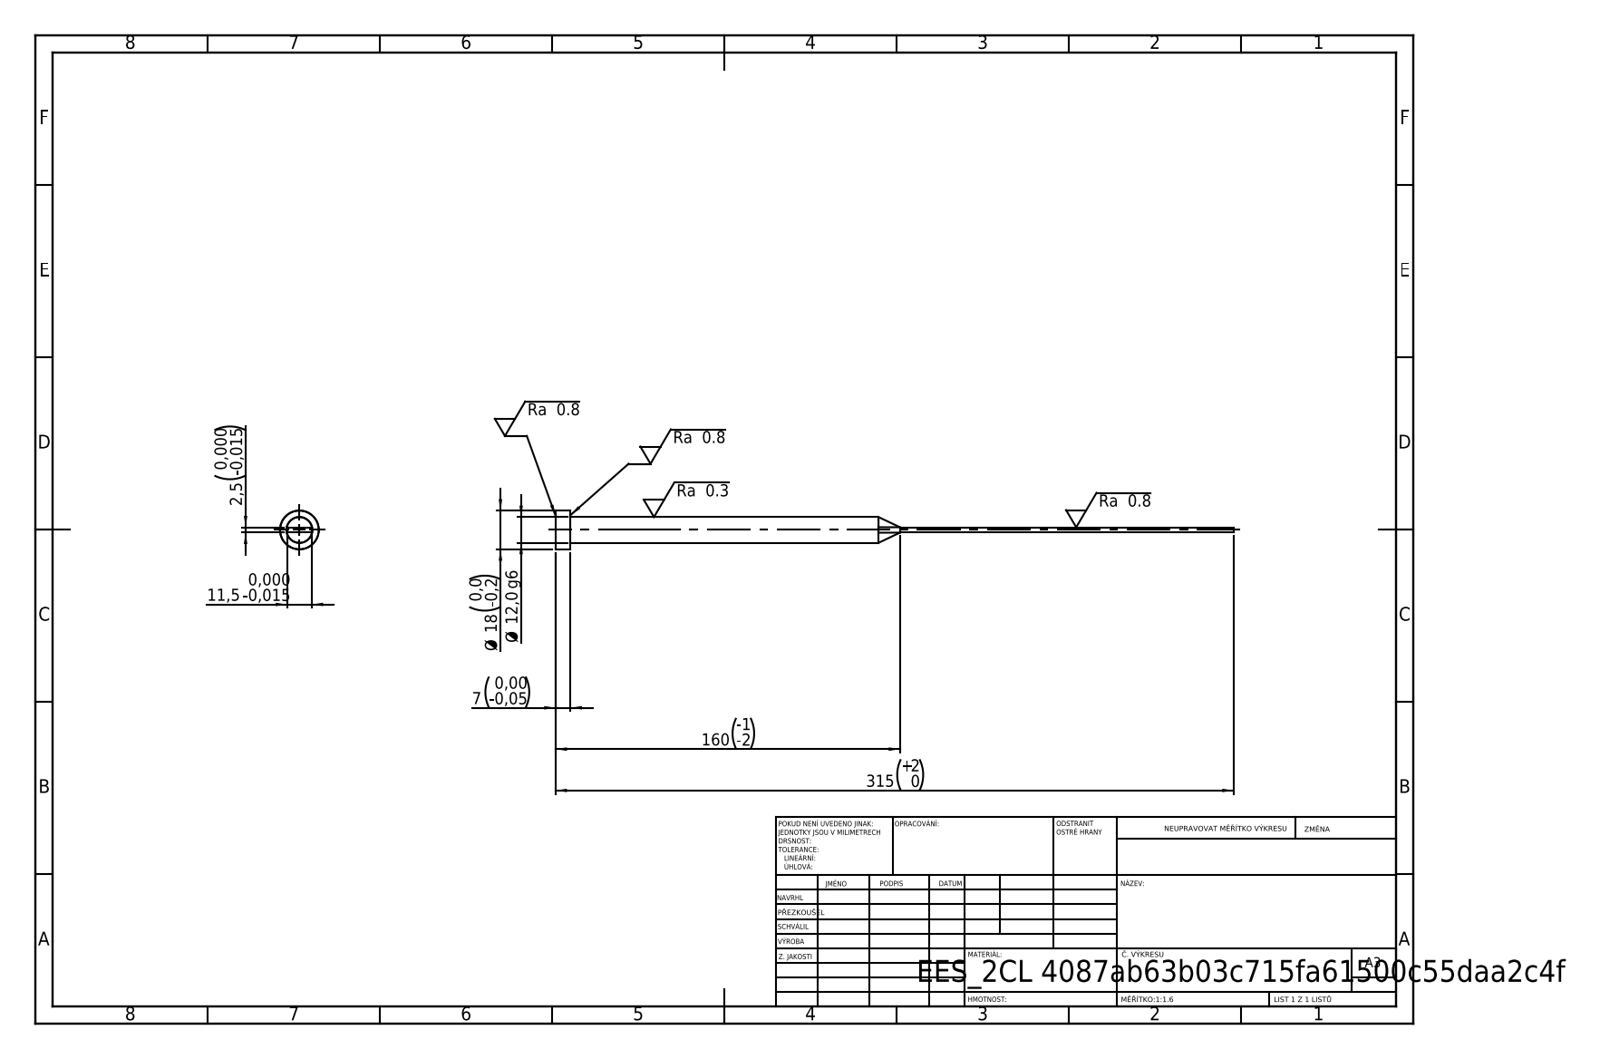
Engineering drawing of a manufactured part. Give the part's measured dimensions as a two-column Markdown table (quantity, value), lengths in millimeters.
| quantity | value |
| --- | --- |
| STEP written by | SolidWorks 2019 (CONFIG_CONTROL_DESIGN) |
| units | millimeters |
| bodies | 1 solid, 15 faces (7 planar, 4 cylindrical, 4 other) |
| overall size | 315 × 18 × 18 |
| volume | 23 090 mm³ |
| surface area | 10 881 mm² |
| round bosses / shafts (diameter × count) | 18 × 1, 12 × 1 |
| main face-to-face distances | 2.5, 11.5, 7, 315, 308 |
